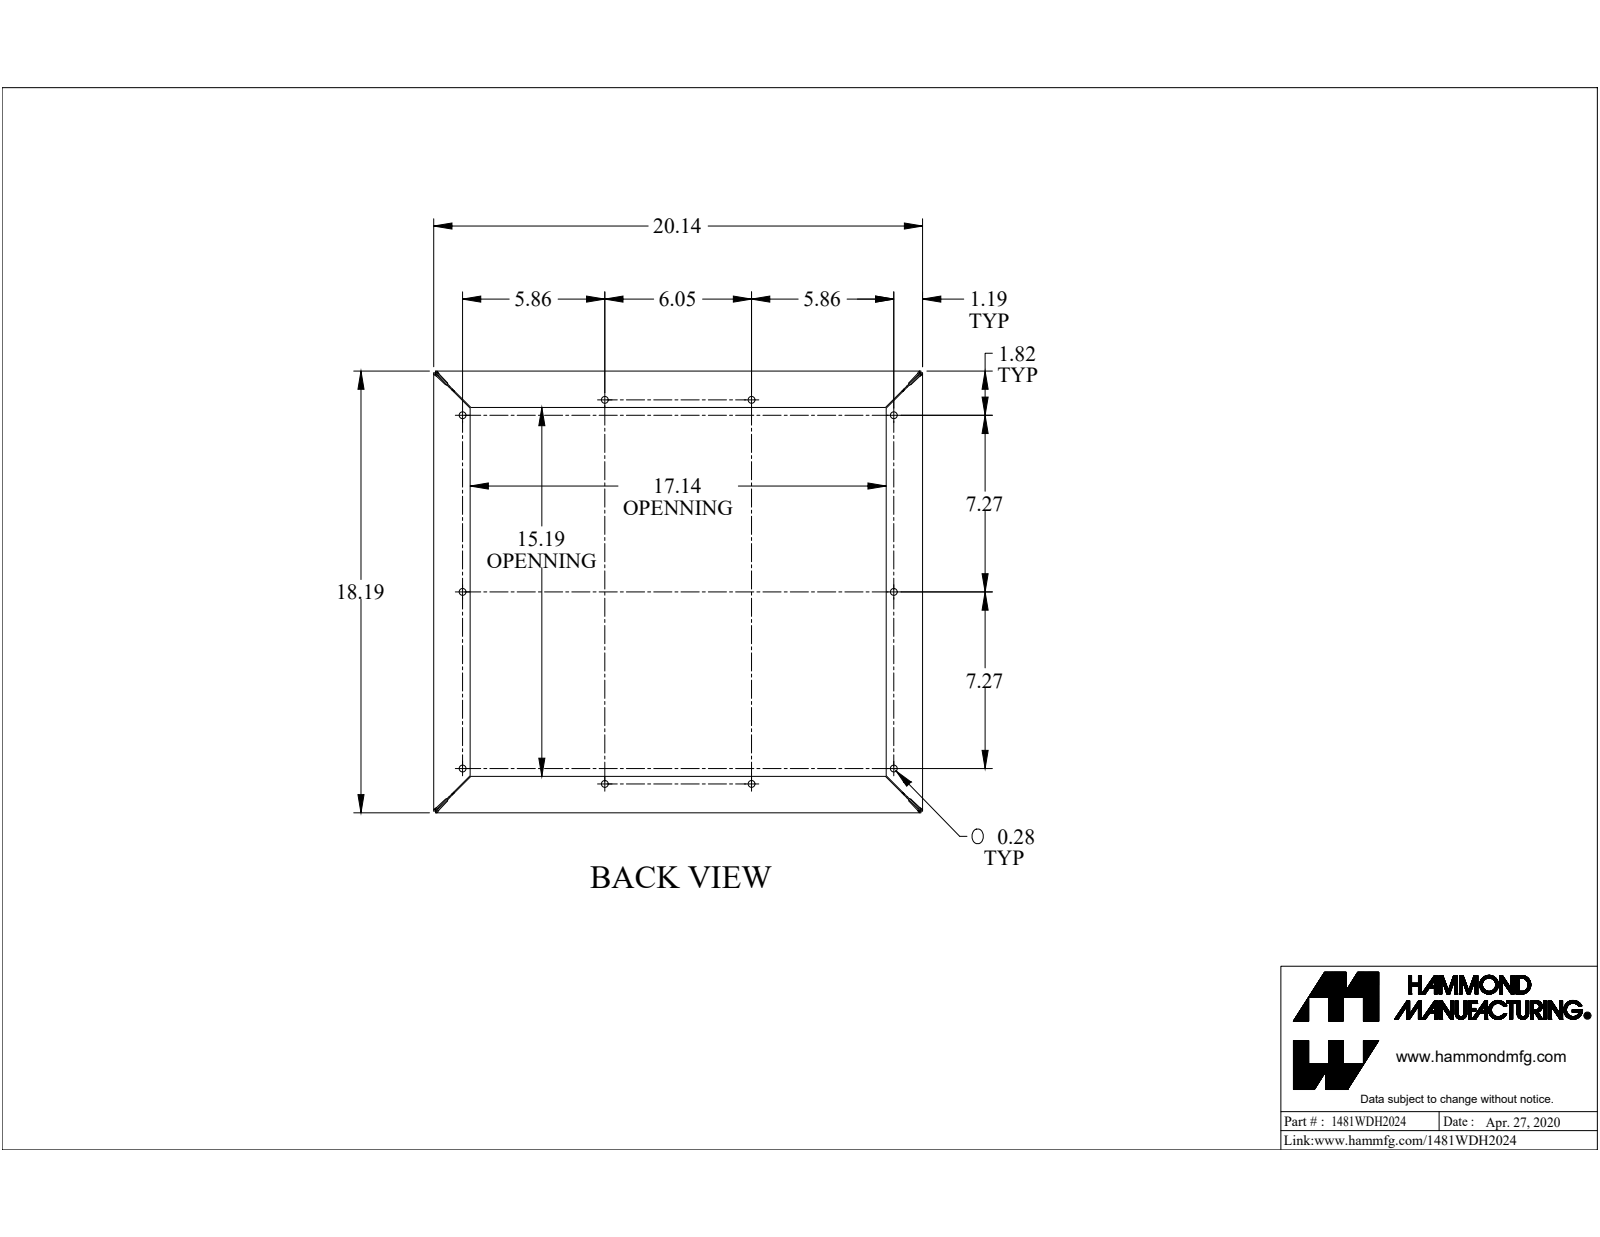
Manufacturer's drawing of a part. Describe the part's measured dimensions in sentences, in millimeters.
The part is named "1481WDH2024". Its 3-D file was written by "SolidWorks 2019 (CONFIG_CONTROL_DESIGN)". It is 60 solids with 1087 faces: 657 planar, 248 cylindrical and 182 other. Overall it measures 511.6 by 462 by 77.7 millimeters. Its volume is 1 865 000 cubic millimeters and its surface area 1 309 000 square millimeters. Round holes: 14 of diameter 3.3, 14 of diameter 6.4, 10 of diameter 7.1, 1 of diameter 4.4, 1 of diameter 5.9, 1 of diameter 6.1, 1 of diameter 6.1, 1 of diameter 15.9, 1 of diameter 19.9. Round bosses or shafts: 15 of diameter 5.7, 14 of diameter 9.3, 14 of diameter 4.2, 1 of diameter 27.9, 1 of diameter 13.3, 1 of diameter 11.6, 1 of diameter 11.6, 1 of diameter 10.1. Partial cylindrical surfaces (rounded edges, fillets, slot ends): 28 of radius 0.9, 28 of radius 2.7, 12 of radius 9.7, 8 of radius 482.7, 4 of radius 0.2, 4 of radius 0.4, 4 of radius 1.6, 4 of radius 2.2. The main face-to-face distances are 1.8, 6.4, 4.5, 65.5, 67.3, 21.4, 44.1, 61, 460.2, 7.6. The hole center spacings are 400.1, 120.7, 261.1, 381.5, 399.7, 426, 435.2, 435.3.
